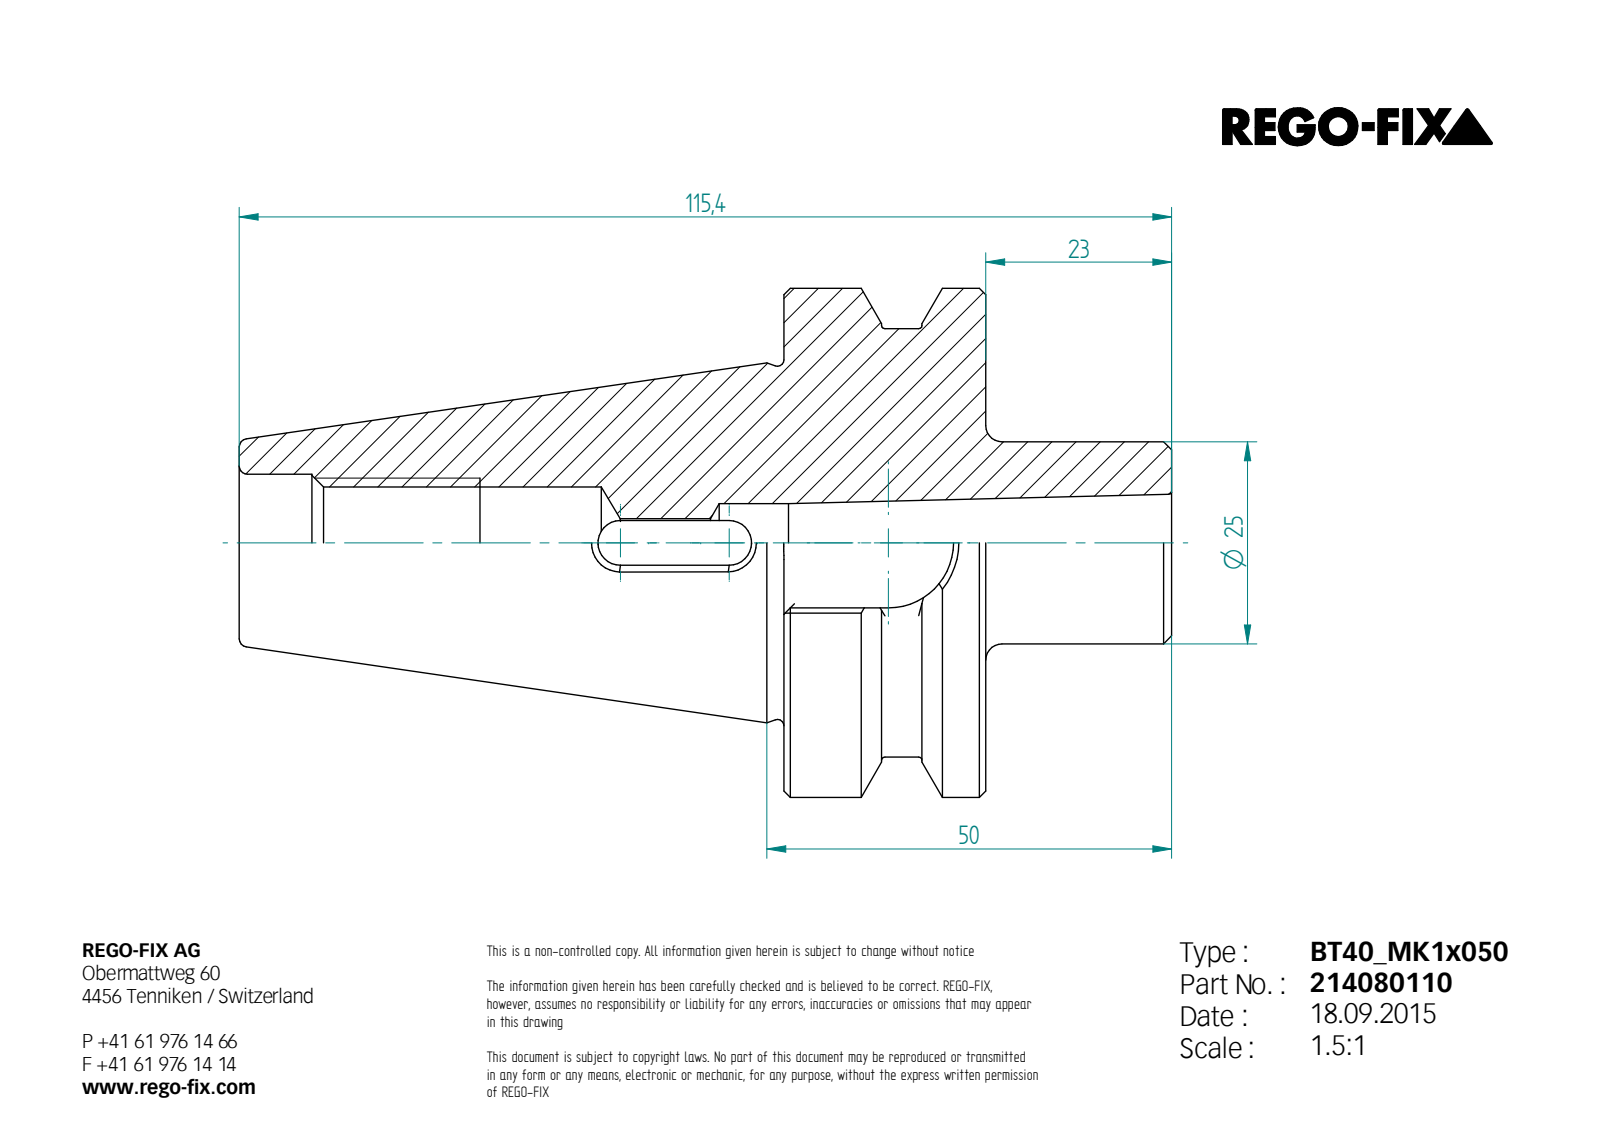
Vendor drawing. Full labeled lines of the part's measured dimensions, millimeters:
STEP written by: Unknown (AUTOMOTIVE_DESIGN)
Units: millimetres
Bodies: 1 solid, 99 faces (40 planar, 22 cylindrical, 37 other)
Overall size (bounding box): 115.4 × 63 × 63
Volume: 129 284 mm³ · Surface area: 25 257 mm²
Round holes (diameter × count): ⌀9.7 ×1, ⌀13.84 ×1, ⌀17 ×1
Round bosses / shafts (diameter × count): ⌀63 ×1, ⌀53 ×1, ⌀25 ×1
Partial cylindrical surfaces — rounded edges, fillets, slot ends (radius × count): R0.5 ×4, R2.77 ×2, R3 ×1, R8.05 ×1
Main face-to-face distances: 25, 5.54, 5.28, 10.82, 48, 23, 45.1, 67.4, 92.4, 115.4
